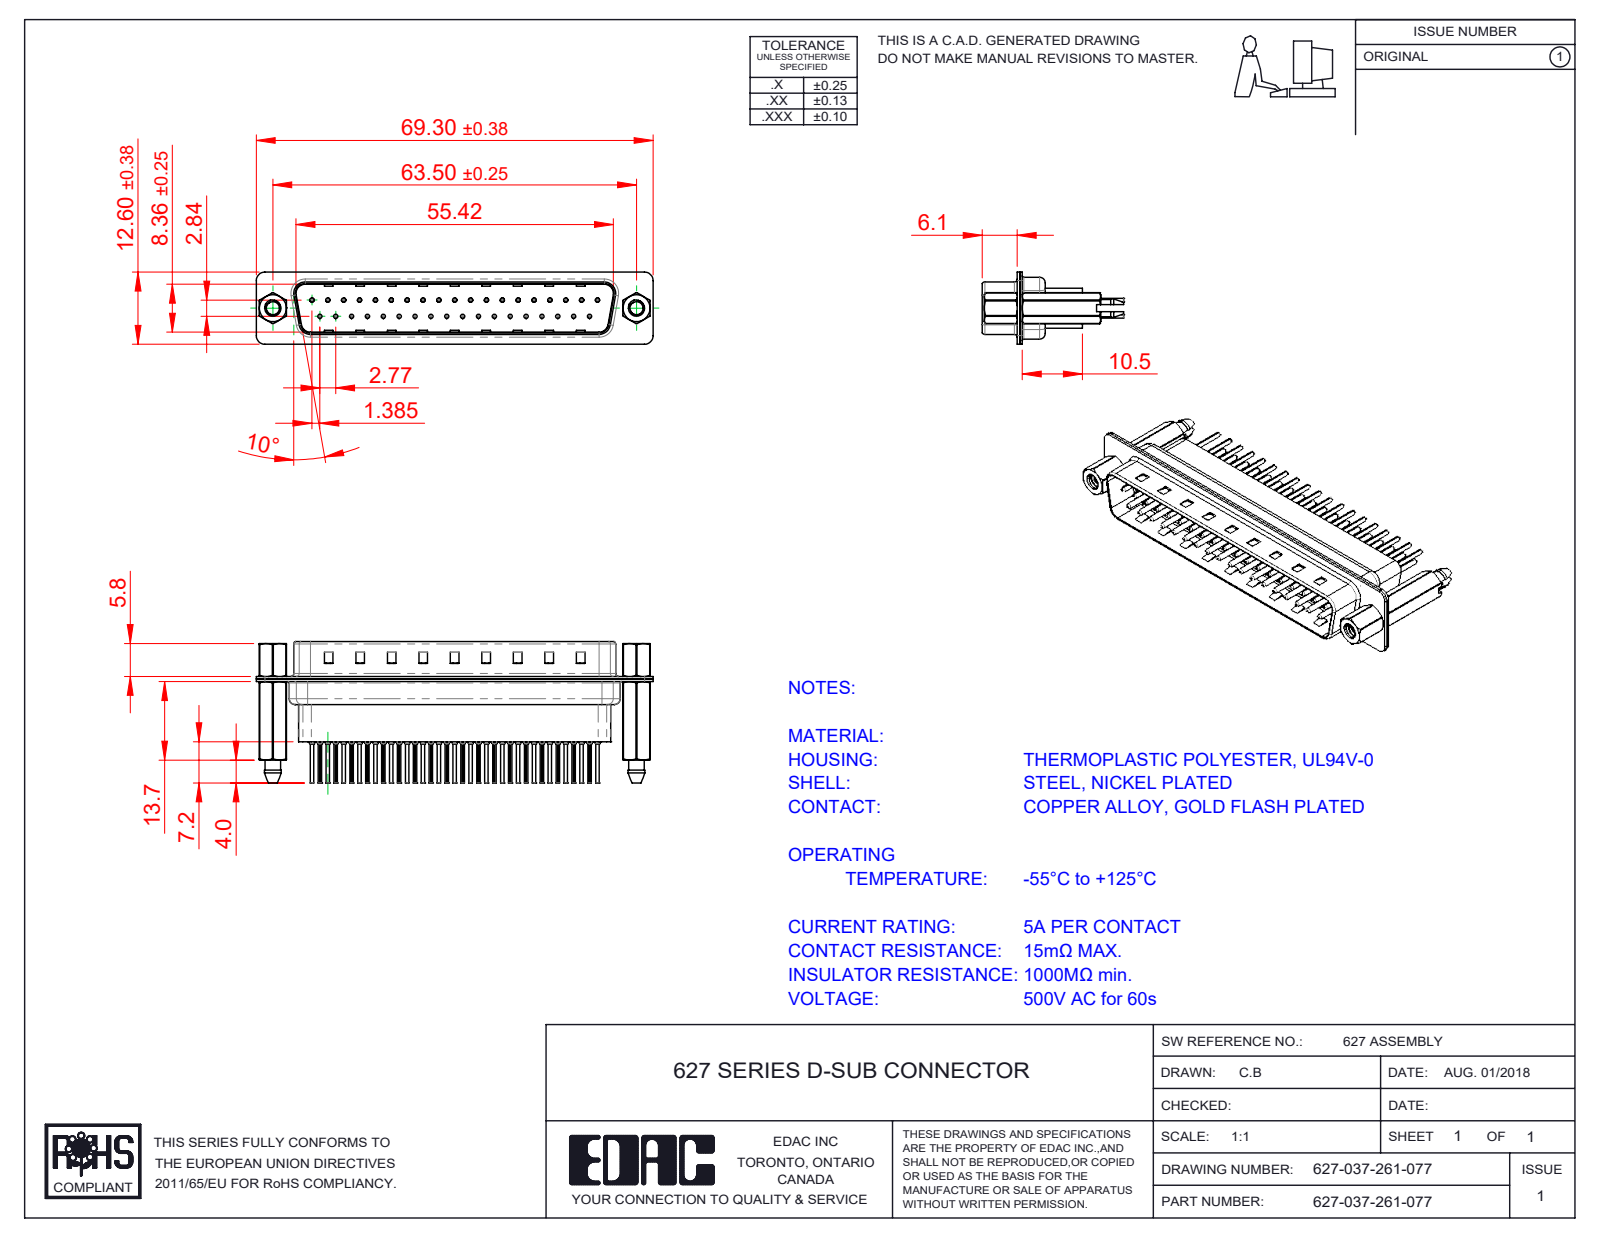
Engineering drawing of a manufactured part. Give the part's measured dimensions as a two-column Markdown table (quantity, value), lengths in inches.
| quantity | value |
| --- | --- |
| part name | 627 4-40 Threaded Boardlock_HP61; 627 Shell Front_37 Contacts; 627 Housing_37 HP; 627 4-40 Hex Standoff (+4 more) |
| STEP written by | SolidWorks 2020 (CONFIG_CONTROL_DESIGN) |
| units | inches |
| bodies | 44 solids, 4272 faces (1145 planar, 1648 cylindrical, 1479 other) |
| overall size | 2.728 × 0.969 × 0.496 |
| volume | 0.36 in³ |
| surface area | 23.51 in² |
| round holes (diameter × count) | 0.008 × 37, 0.014 × 37, 0.043 × 37, 0.063 × 37, 0.089 × 2, 0.09 × 2, 0.157 × 2, 0.189 × 2 |
| round bosses / shafts (diameter × count) | 0.079 × 37, 0.059 × 37, 0.03 × 37, 0.024 × 37, 0.193 × 2, 0.11 × 2 |
| partial cylindrical surfaces (radius × count) | 0.004 × 74, 0.059 × 18, 0.079 × 12, 0.063 × 10, 0.02 × 8, 0.01 × 4, 0.024 × 4, 0.026 × 4 |
| main face-to-face distances | 0.016, 0.032, 0.377, 0.018, 0.027, 0.302, 0.059, 0.043, 0.318, 0.345 |
| hole center spacings | 0.124, 0.109, 0.218, 0.327, 0.198, 0.398, 0.436, 0.503 |
